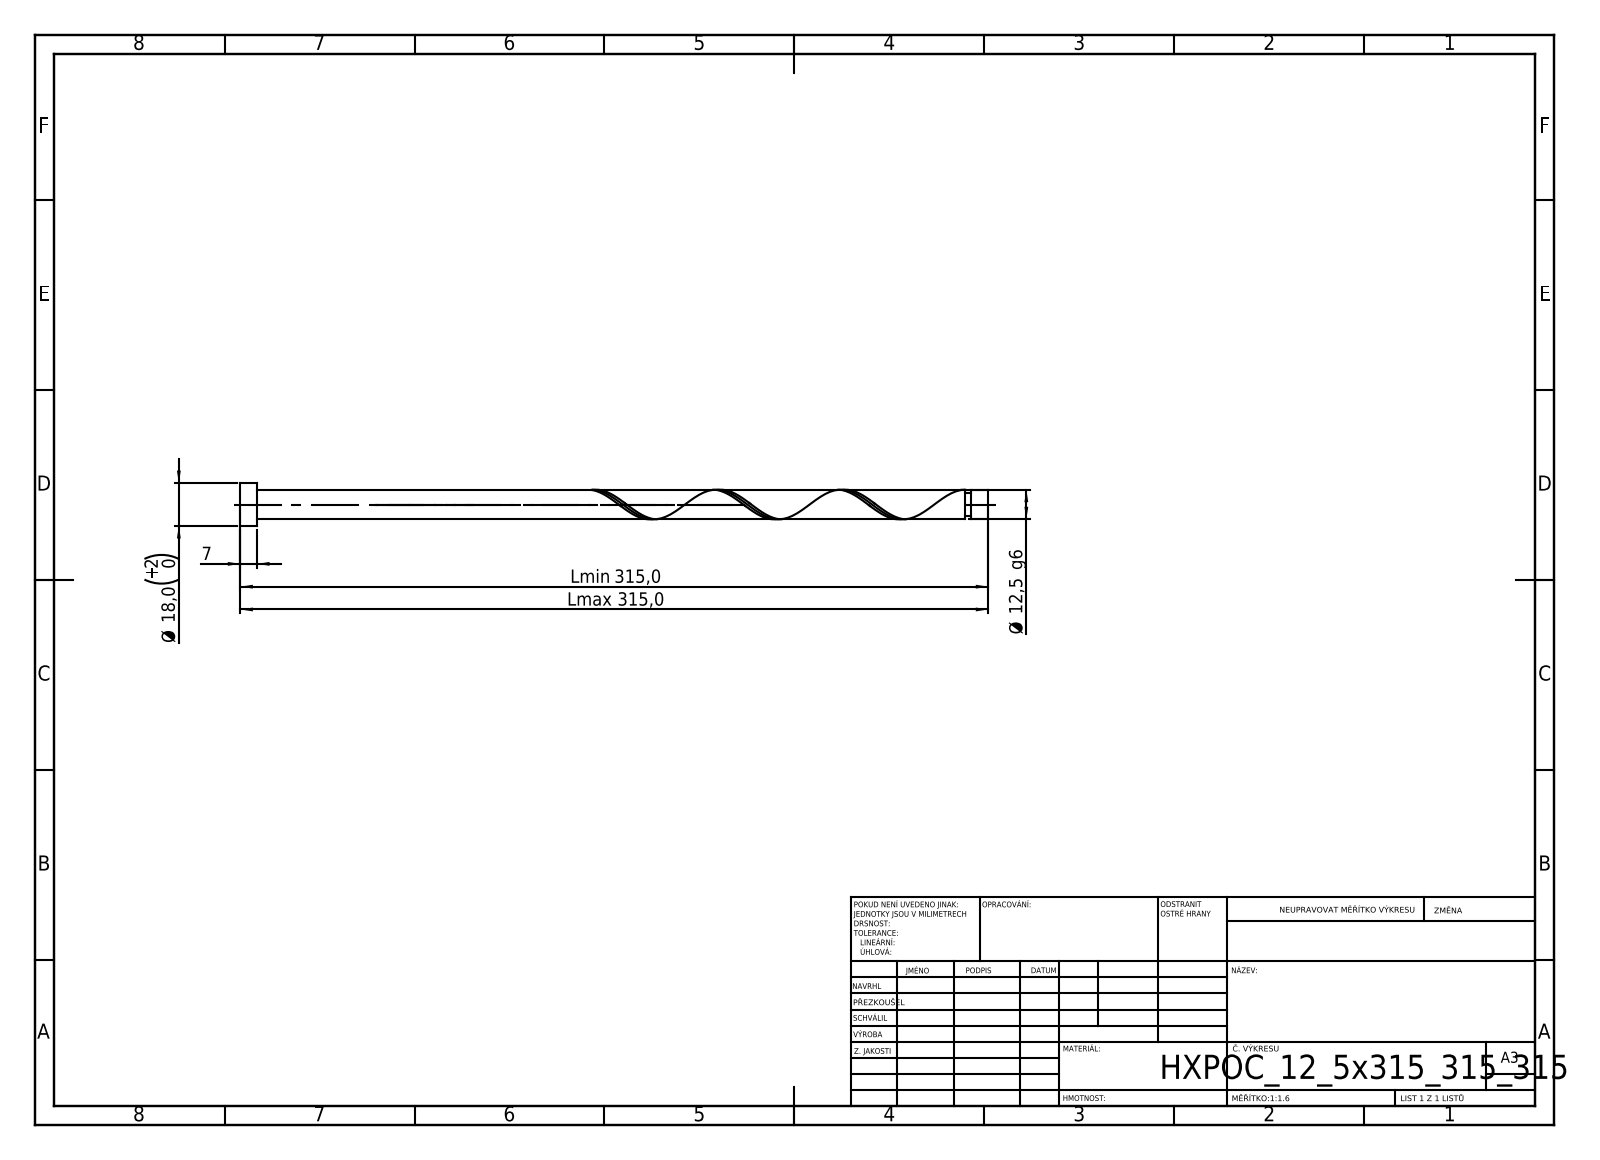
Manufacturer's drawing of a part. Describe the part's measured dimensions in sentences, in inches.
Its 3-D file was written by "SolidWorks 2019 (CONFIG_CONTROL_DESIGN)". It is 1 solid with 21 faces: 6 planar, 14 cylindrical and 1 other. Overall it measures 12.402 by 0.709 by 0.709 inches. Its volume is 2.386 cubic inches and its surface area 20.65 square inches. Round bosses or shafts: 1 of diameter 0.709, 1 of diameter 0.492, 1 of diameter 0.394. The main face-to-face distances are 0.276, 12.402, 12.126, 12.121, 11.846, 0.28, 12.023, 11.747, 0.098, 0.379.
